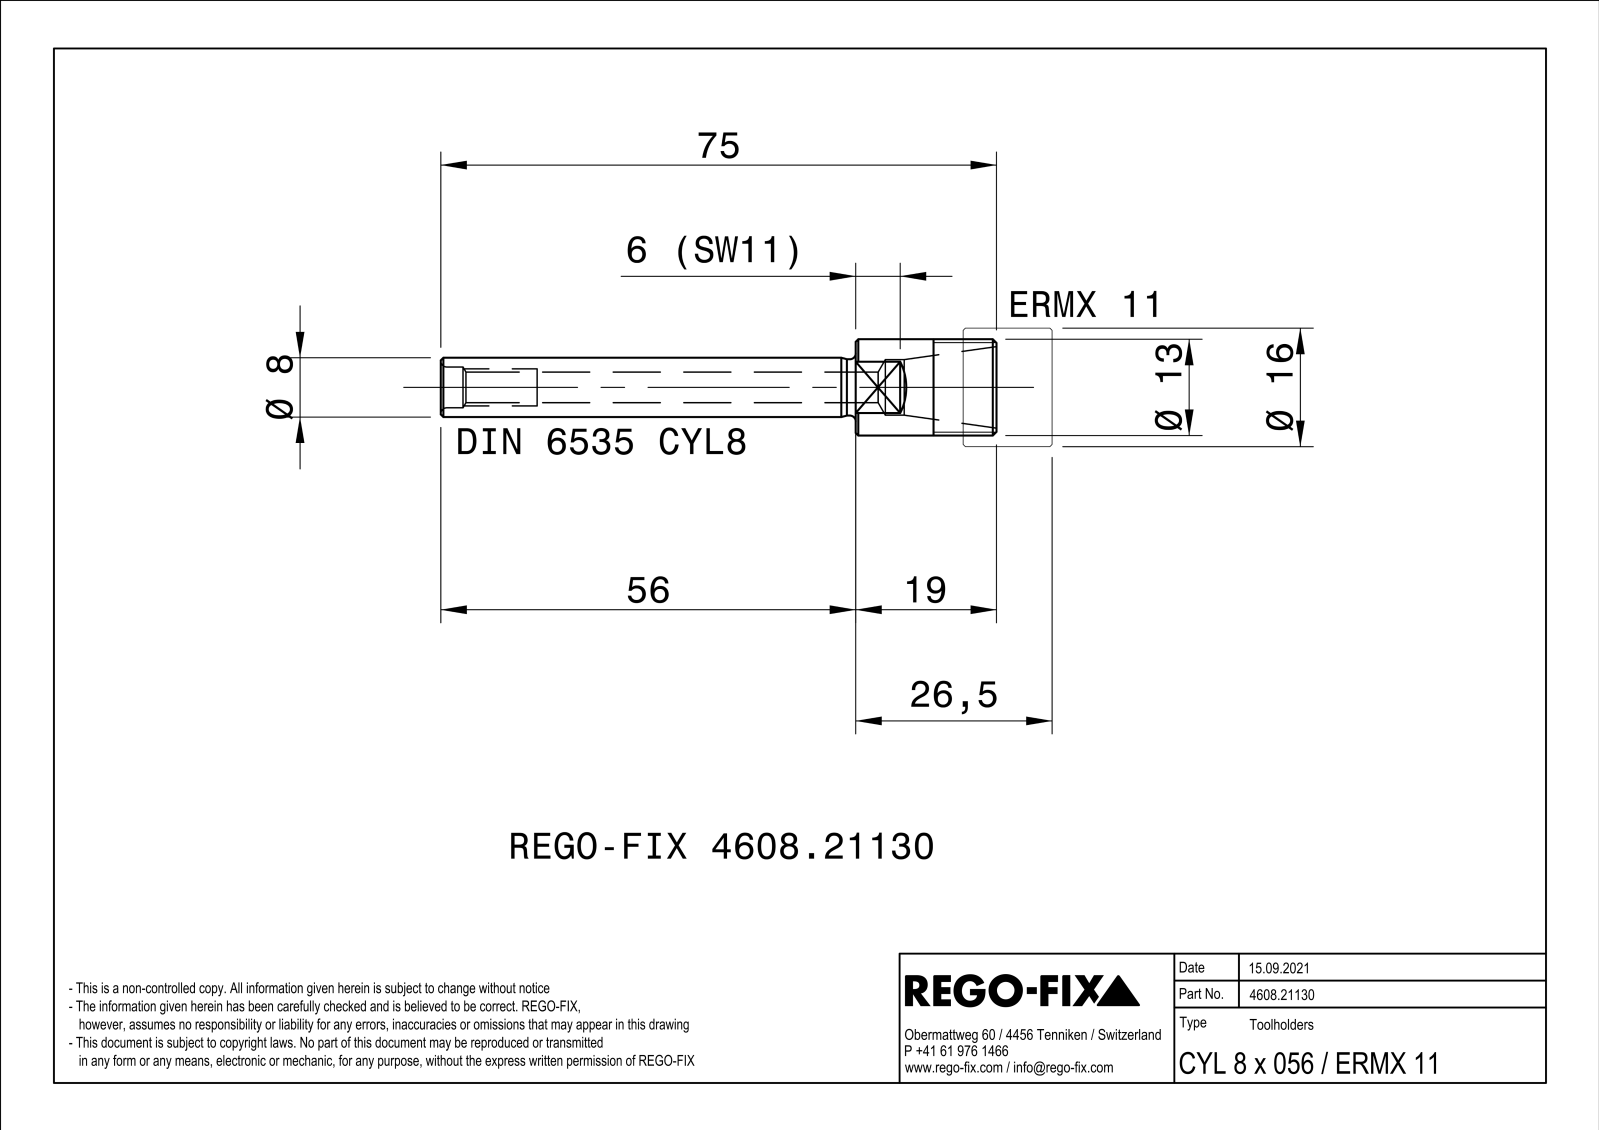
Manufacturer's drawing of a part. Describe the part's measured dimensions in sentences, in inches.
The part is named "0023895". Its 3-D file was written by "SIEMENS PLM Software Solid Edge ST10 (AUTOMOTIVE_DESIGN)". It is 1 solid with 28 faces: 9 planar, 8 cylindrical and 11 other. Overall it measures 2.953 by 0.512 by 0.512 inches. Its volume is 0.211 cubic inches and its surface area 5.468 square inches. Round holes: 1 of diameter 0.163, 1 of diameter 0.217, 1 of diameter 0.295. Round bosses or shafts: 1 of diameter 0.512, 1 of diameter 0.315, 1 of diameter 0.299. The main face-to-face distances are 0.433, 0.748, 0.159, 2.953, 2.205.
